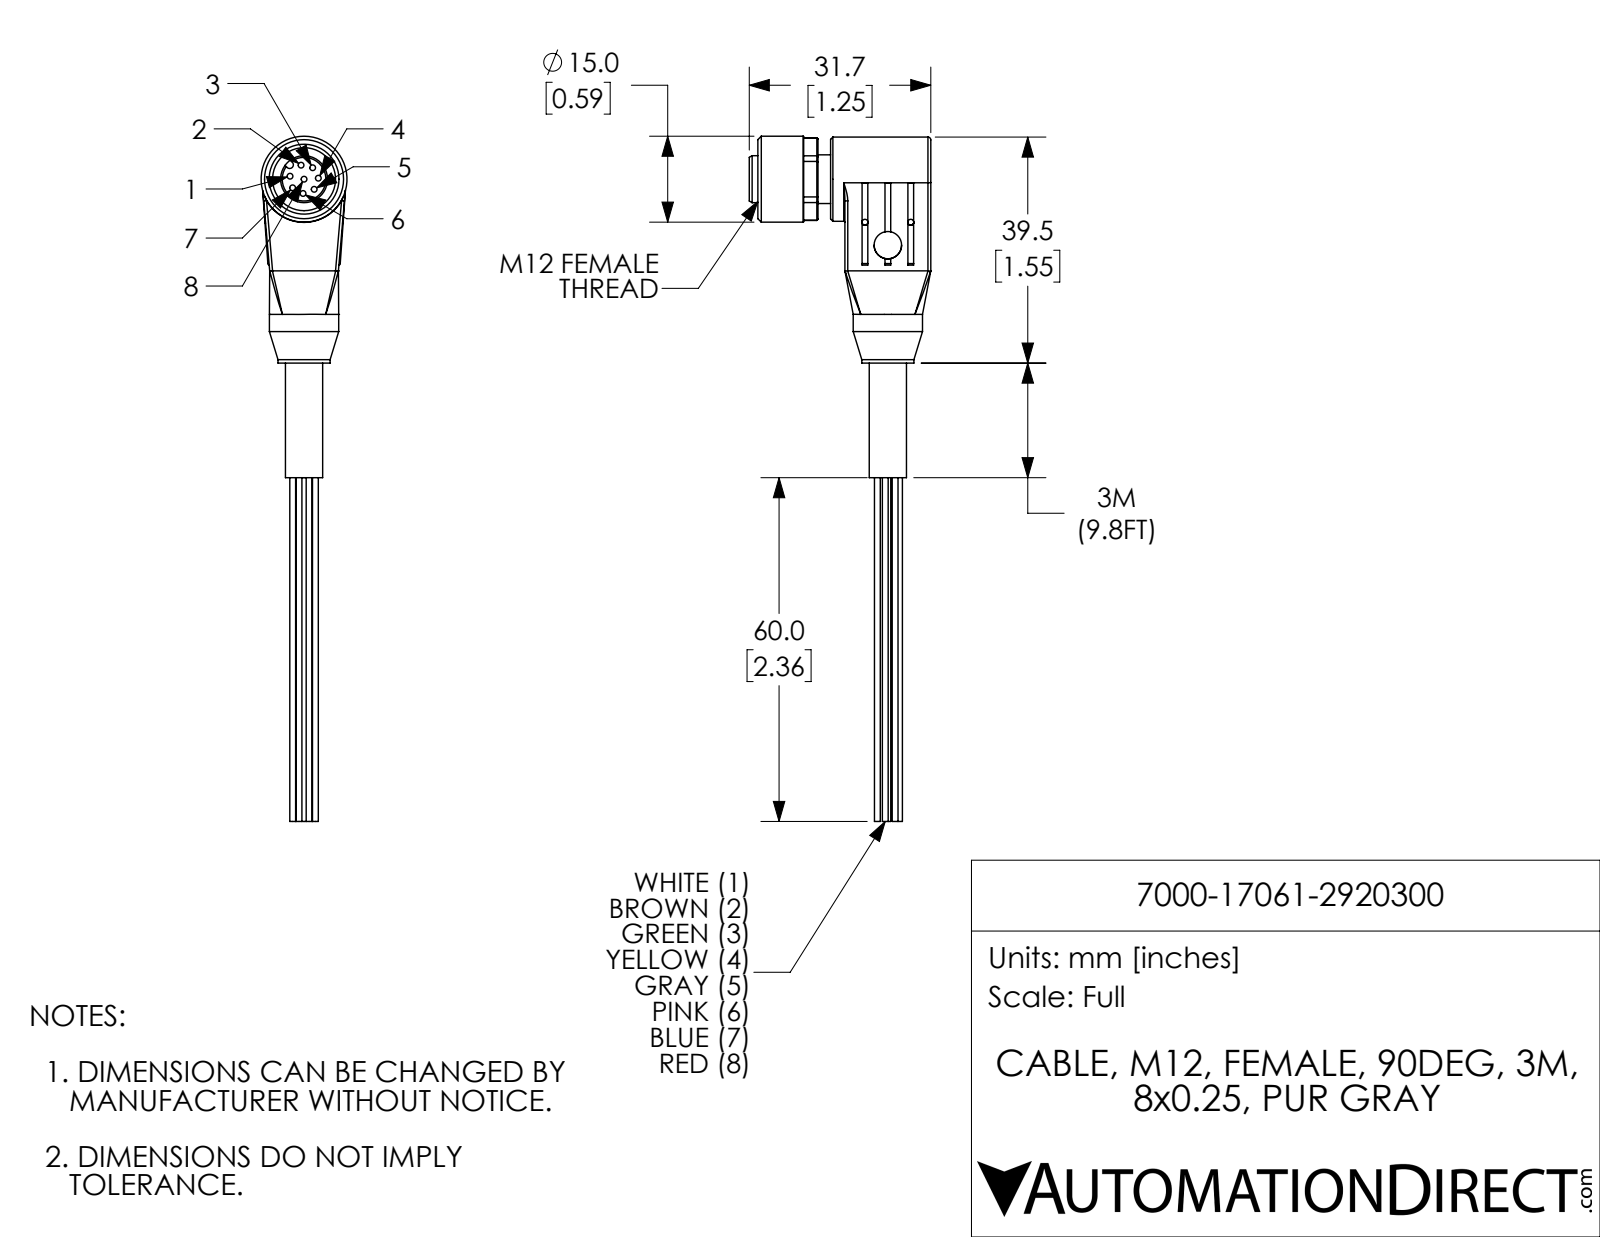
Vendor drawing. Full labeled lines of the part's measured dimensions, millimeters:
Part name (STEP PRODUCT): 7000-17061-2920300
STEP written by: SolidWorks 2017 (AUTOMOTIVE_DESIGN)
Units: millimetres
Bodies: 1 solid, 189 faces (81 planar, 75 cylindrical, 33 other)
Overall size (bounding box): 119.6 × 31.7 × 15
Volume: 9 490 mm³ · Surface area: 5 616 mm²
Round holes (diameter × count): ⌀1 ×8, ⌀1 ×4, ⌀4.8 ×1, ⌀11 ×1
Round bosses / shafts (diameter × count): ⌀1 ×8, ⌀15 ×1, ⌀14.7 ×1, ⌀12.1 ×1, ⌀9.1 ×1, ⌀8.5 ×1, ⌀8.2 ×1, ⌀6.5 ×1
Partial cylindrical surfaces — rounded edges, fillets, slot ends (radius × count): R0.5 ×4, R0.3 ×2, R0.7 ×1, R7.2 ×1
Main face-to-face distances: 2.5, 15, 4.7, 17.5, 19.7, 2.2, 3, 7.7, 12, 16.7
Hole centre spacings: 2.5, 2.1, 3.8, 5, 2.1, 4.2, 4.8, 4.8
